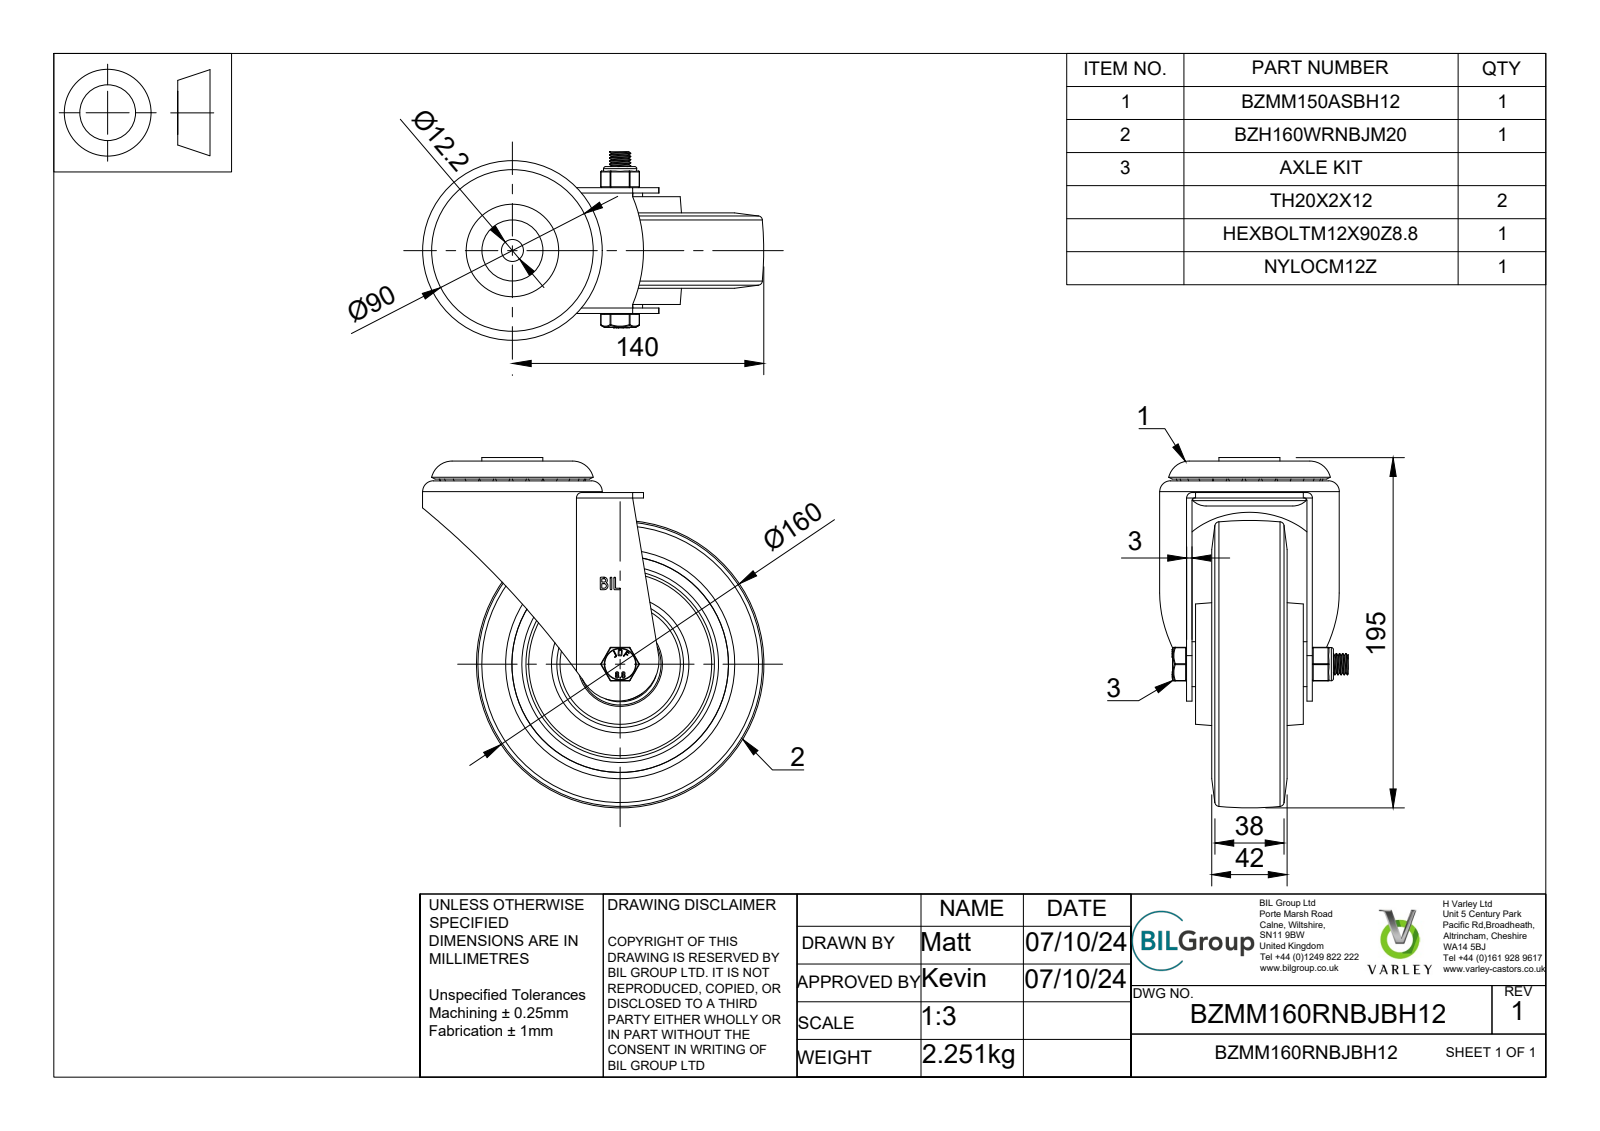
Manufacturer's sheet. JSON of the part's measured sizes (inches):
{"part_name": "BZMM160RNBJBH12 v3; BZMM150ASBH12 - 64 v1; ZINC PLATED, PRESSED STEEL FORKS; ZINC PLATED, PRESSED STEEL HEAD (+6 more)", "step_written_by": "Autodesk Translation Framework v13.20.0.188 (AUTOMOTIVE_DESIGN)", "units": "inches", "bodies": {"solids": 81, "faces": 1094, "planar": 415, "cylindrical": 193, "other": 486}, "overall_size": [7.677, 7.48, 4.134], "volume_in3": 49.77, "surface_area_in2": 394.9, "round_holes": [[0.48, 2], [0.472, 1], [0.492, 1], [0.551, 1], [0.787, 1], [1.122, 1], [1.213, 1], [1.535, 1], [1.587, 1], [1.594, 1], [1.654, 1], [1.85, 1]], "round_bosses_or_shafts": [[0.945, 2], [3.937, 1], [2.48, 1], [1.606, 1], [1.339, 1], [1.232, 1], [1.063, 1], [0.984, 1]], "partial_cylinders_radius": [[0.02, 20], [0.019, 4], [0.035, 4], [0.059, 4], [0.035, 2], [0.035, 2], [0.118, 2], [0.267, 2]], "face_to_face_distances": [0.118, 0.551, 2.638, 0.433, 0.197, 0.984, 1.22, 1.535, 1.102, 1.417]}
